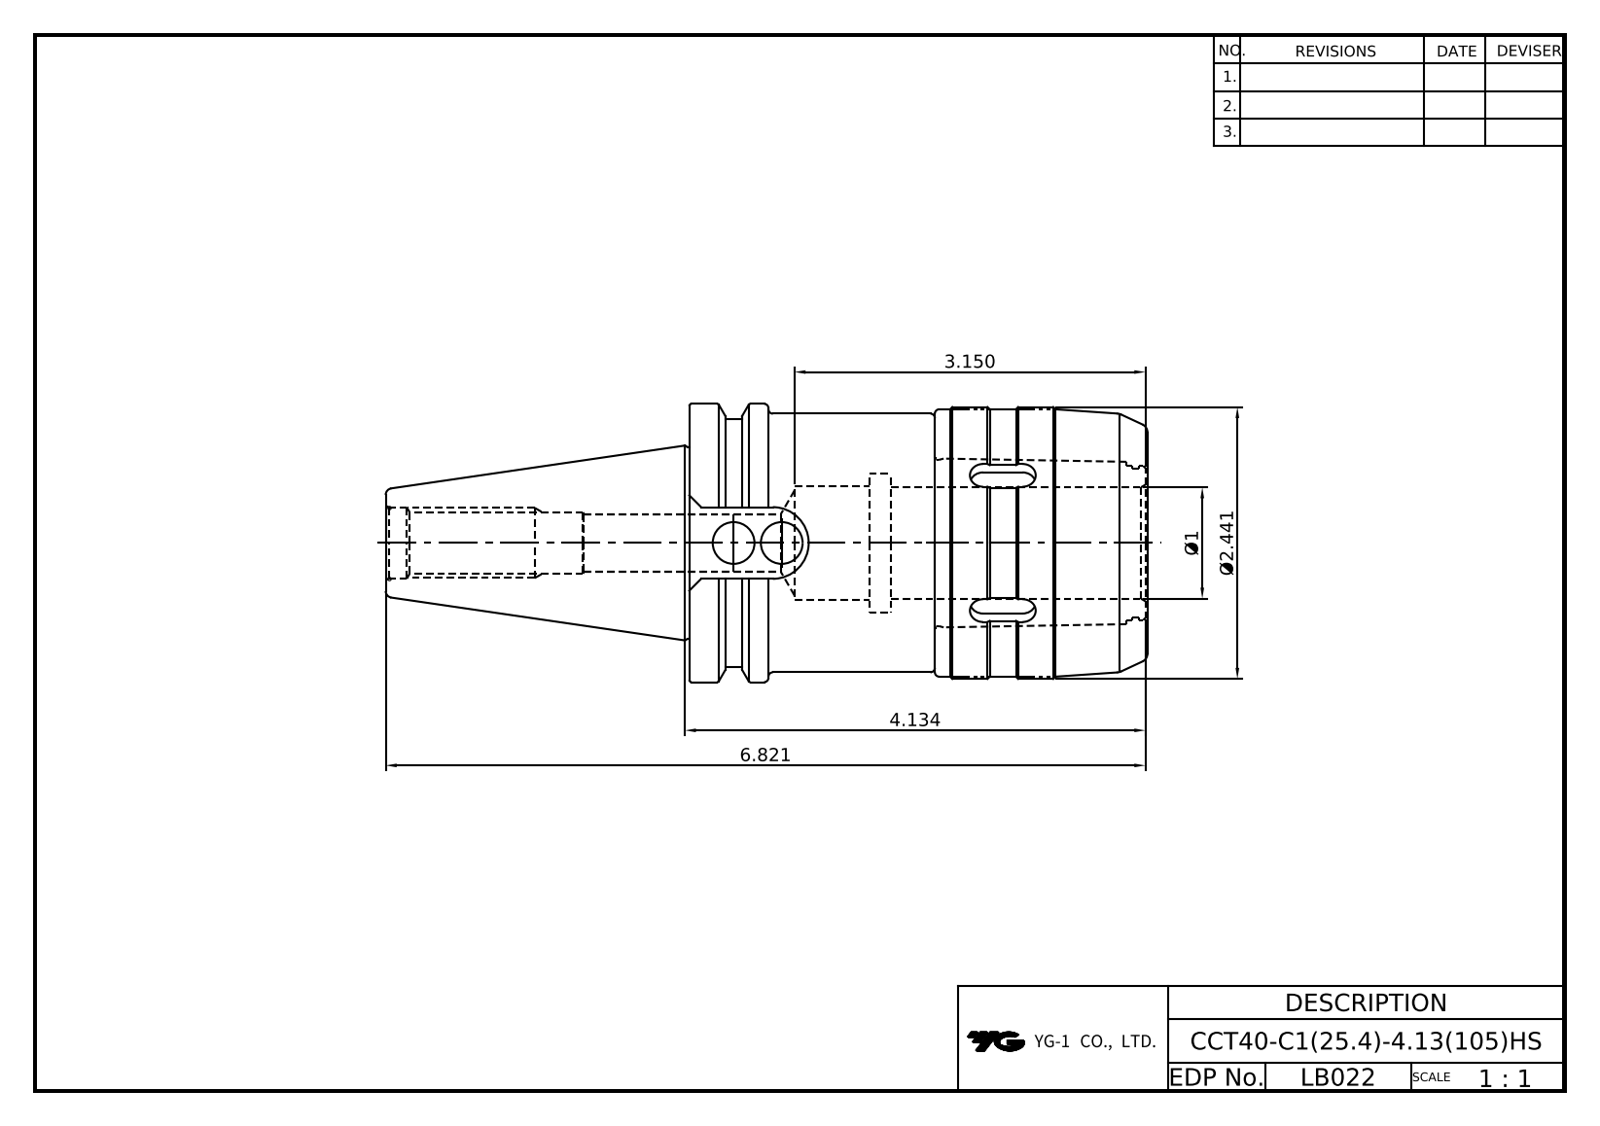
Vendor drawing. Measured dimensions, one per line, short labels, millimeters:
name: CCT40-C25.4-105HS; C25-CAP
written by: Autodesk Inventor 2022 (AUTOMOTIVE_DESIGN)
unit: mm
bodies: 2 solids, 176 faces (79 planar, 44 cylindrical, 53 other)
size: 173.75 × 63.5 × 62
volume: 287 174 mm³; area: 60 052 mm²
holes: 1× ⌀9.53, 1× ⌀13, 1× ⌀13.39, 1× ⌀16.3, 1× ⌀25.4, 1× ⌀26, 1× ⌀31.6, 1× ⌀44.5, 1× ⌀46.45
bosses: 1× ⌀63.5, 1× ⌀62, 1× ⌀61, 1× ⌀59, 1× ⌀56.3, 1× ⌀43.8, 1× ⌀35.2
rounds: 6× R3, 1× R8.19
face distances: 56, 104.5, 48.5, 104, 48, 0.5, 24, 32, 80, 80.5
